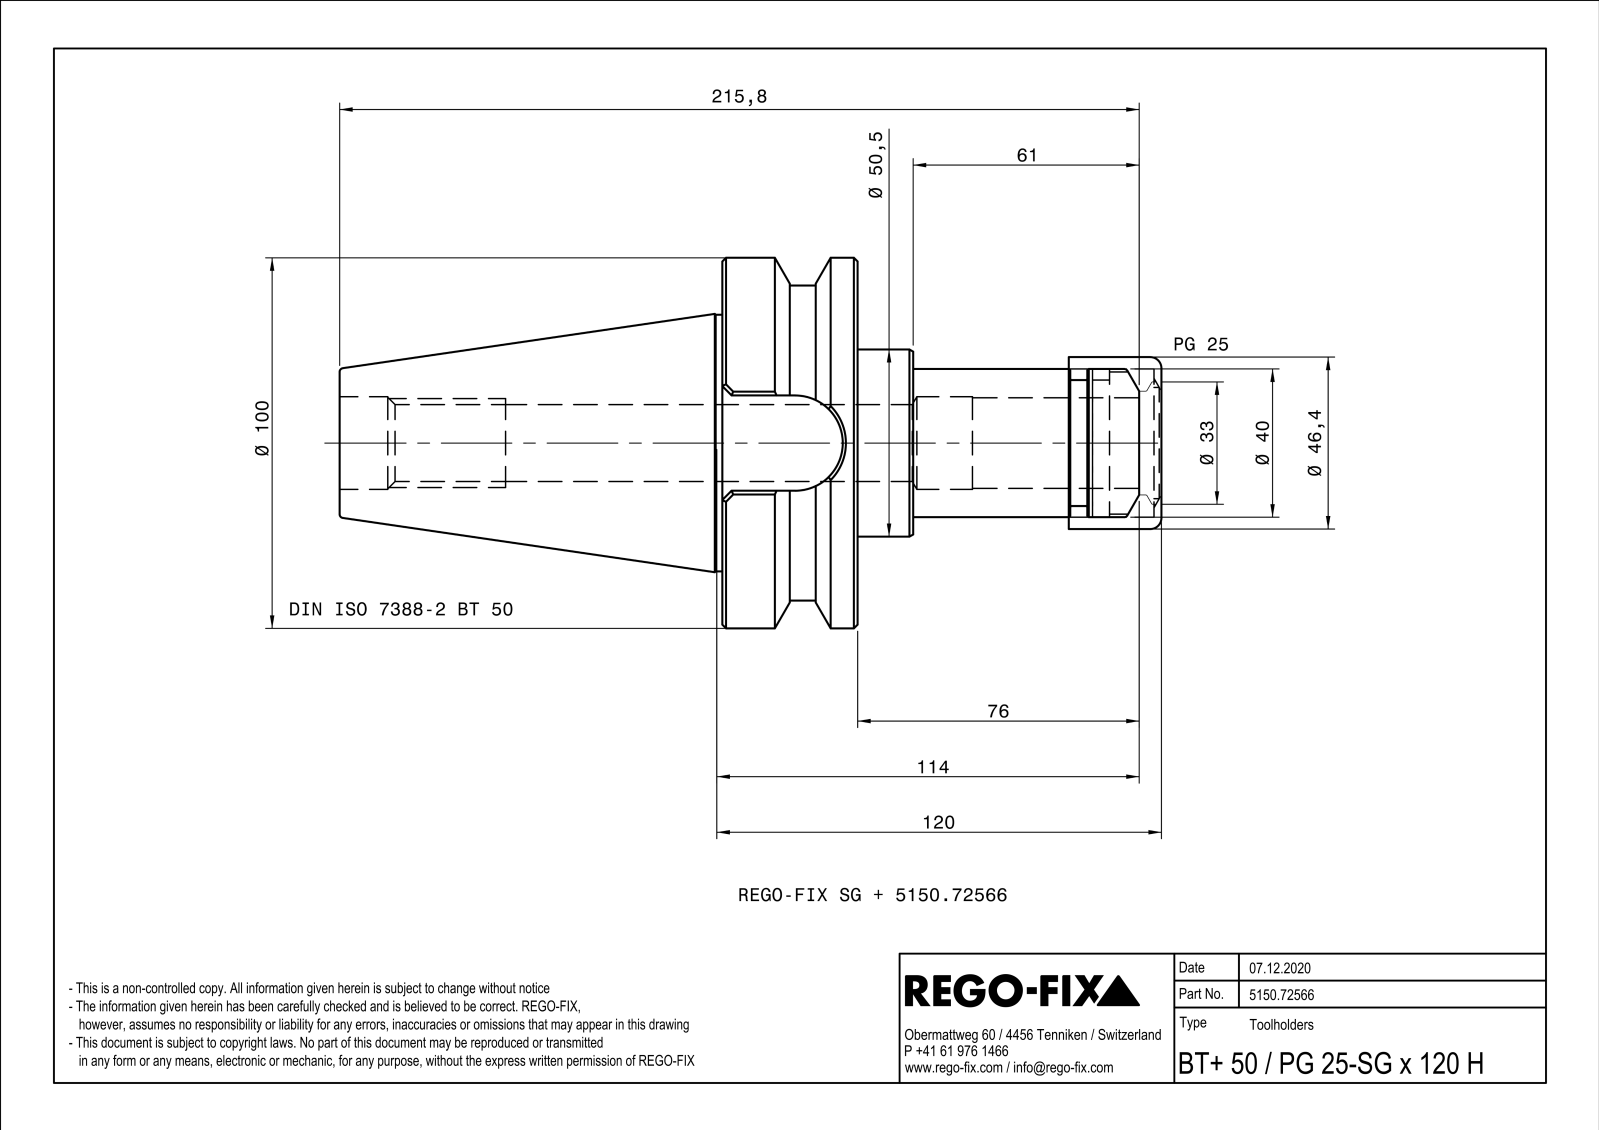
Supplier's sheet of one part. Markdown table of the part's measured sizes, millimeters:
| quantity | value |
| --- | --- |
| part name | 0010011 |
| STEP written by | SIEMENS PLM Software Solid Edge ST10 (AUTOMOTIVE_DESIGN) |
| units | millimeters |
| bodies | 2 solids, 109 faces (31 planar, 30 cylindrical, 48 other) |
| overall size | 221.8 × 100 × 100 |
| volume | 529 003 mm³ |
| surface area | 77 600 mm² |
| round holes (diameter × count) | 20.75 × 1, 25 × 1, 30 × 1, 38.38 × 1, 40.05 × 1, 42 × 1 |
| round bosses / shafts (diameter × count) | 100 × 1, 85 × 1, 69.25 × 1, 50.5 × 1, 46.4 × 1, 46 × 1, 40 × 1, 34 × 1 |
| partial cylindrical surfaces (radius × count) | 0.5 × 8, 12.85 × 1 |
| main face-to-face distances | 36.5, 70.7, 139.8, 103.3, 82, 118.5, 221.8, 67, 15, 51.5 |
